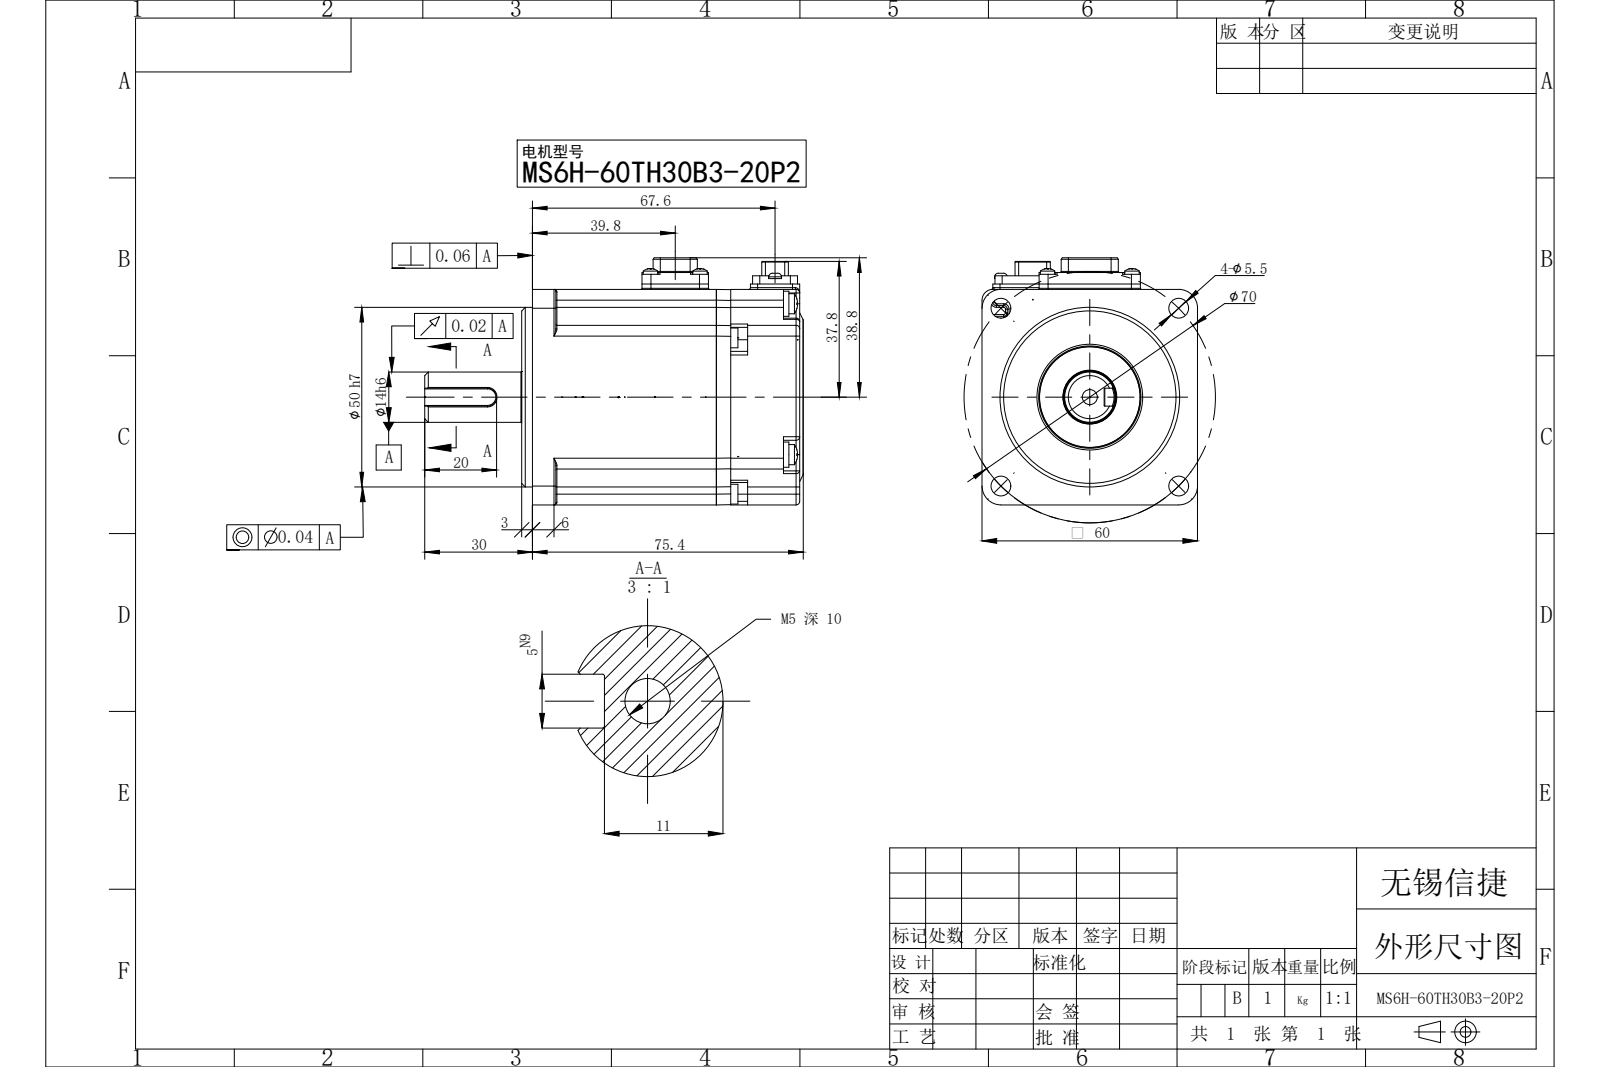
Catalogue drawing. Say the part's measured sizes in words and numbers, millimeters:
The part is named "MS6H-60TH30B3-20P2". Its 3-D file was written by "SolidWorks 2022 (CONFIG_CONTROL_DESIGN)". It is 0 solids with 804 faces: 405 planar, 269 cylindrical and 130 other. Overall it measures 105.4 by 68.8 by 60 millimeters. Round holes: 4 of diameter 2.1, 4 of diameter 5.5, 2 of diameter 1.6, 1 of diameter 4.2, 1 of diameter 15. Round bosses or shafts: 4 of diameter 7, 4 of diameter 5.6, 4 of diameter 5.5, 4 of diameter 4, 2 of diameter 3.5, 1 of diameter 50, 1 of diameter 28, 1 of diameter 14.8. Partial cylindrical surfaces (rounded edges, fillets, slot ends): 38 of radius 1, 24 of radius 0.5, 21 of radius 0.3, 20 of radius 0.2, 17 of radius 3, 12 of radius 2, 10 of radius 0.45, 8 of radius 5. The main face-to-face distances are 60, 75.4, 74.4, 3, 1, 78.4, 77.4, 10, 20.2, 19.2. The hole center spacings are 35, 49.5, 8, 16.6, 18.43, 70, 23.5, 24.16.
